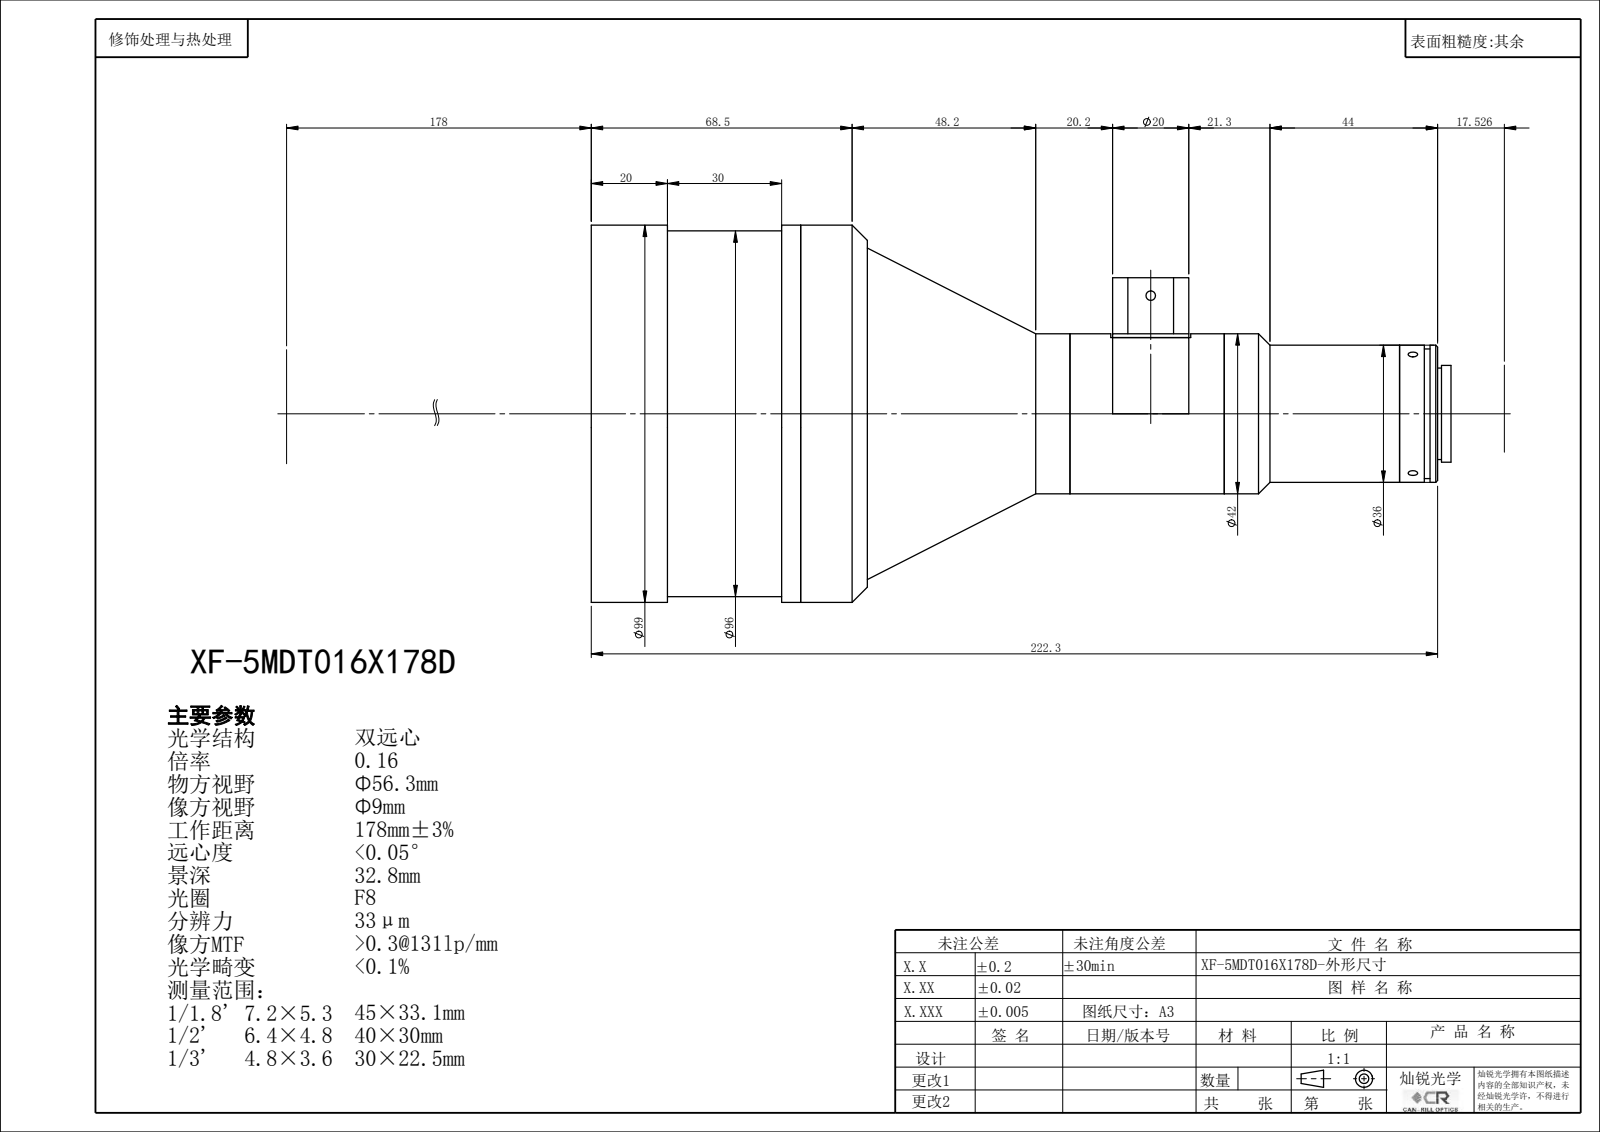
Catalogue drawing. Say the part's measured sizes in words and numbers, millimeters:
The part is named "XF-5MDT016X178D". Its 3-D file was written by "SolidWorks 2014 (CONFIG_CONTROL_DESIGN)". It is 0 solids with 143 faces: 54 planar, 73 cylindrical and 16 other. Overall it measures 225.76 by 99 by 99 millimeters. Round holes: 8 of diameter 2.5, 4 of diameter 3.5, 1 of diameter 14, 1 of diameter 16, 1 of diameter 19.4, 1 of diameter 21.4, 1 of diameter 85, 1 of diameter 87, 1 of diameter 92. Round bosses or shafts: 1 of diameter 99, 1 of diameter 96, 1 of diameter 42, 1 of diameter 36, 1 of diameter 34, 1 of diameter 25.4, 1 of diameter 24. Partial cylindrical surfaces (rounded edges, fillets, slot ends): 4 of radius 4. The main face-to-face distances are 55, 20, 136.92, 5, 220.26, 165.26, 9.53, 45.47, 210.73, 72.5. The hole center spacings are 19.31, 14, 36, 38.63, 75.5.
